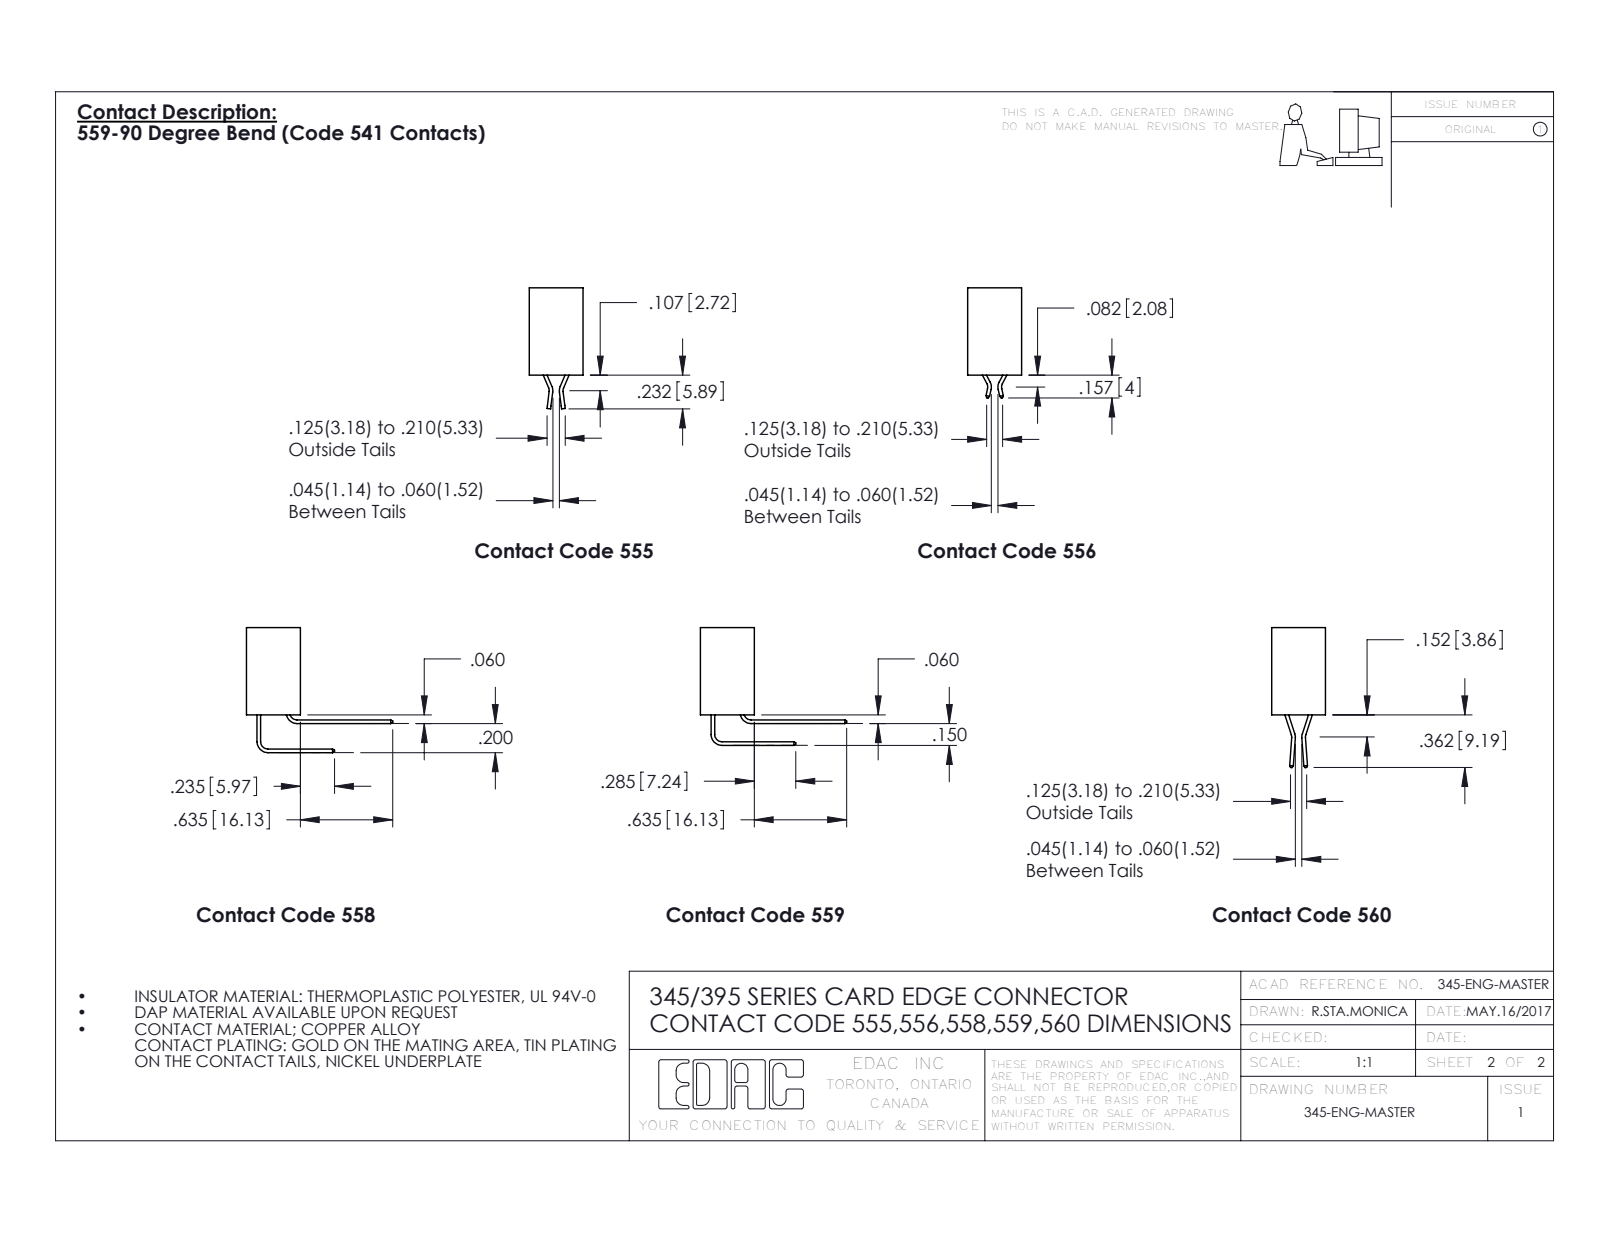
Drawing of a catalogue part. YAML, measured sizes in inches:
part_name: "345 Part_Flush Mounting Lugs - 0.156 Dia-TH; 345-250-001_345-250-001-102; 345-220-058_345-220-058; 395-014-560-258 (+1 more)"
step_written_by: "SolidWorks 2016 (CONFIG_CONTROL_DESIGN)"
units: inches
bodies: {solids: 19, faces: 1110, planar: 690, cylindrical: 360, other: 60}
overall_size: [3.362, 2.079, 0.37]
volume: 0.816
surface_area: 18.38
round_holes:
  - {diameter: 0.089, count: 2}
  - {diameter: 0.125, count: 2}
  - {diameter: 0.156, count: 2}
  - {diameter: 0.064, count: 1}
round_bosses_or_shafts:
  - {diameter: 0.155, count: 2}
partial_cylinders:
  - {radius: 0.01, count: 22}
  - {radius: 0.006, count: 21}
  - {radius: 0.06, count: 16}
  - {radius: 0.007, count: 6}
  - {radius: 0.031, count: 6}
  - {radius: 0.026, count: 3}
  - {radius: 0.01, count: 2}
  - {radius: 0.014, count: 2}
face_to_face_distances: [0.37, 0.15, 0.22, 0.072, 0.077, 0.148, 0.298, 1.496, 0.025, 0.2]
hole_center_spacings: [0.27, 1.045, 1.275]
